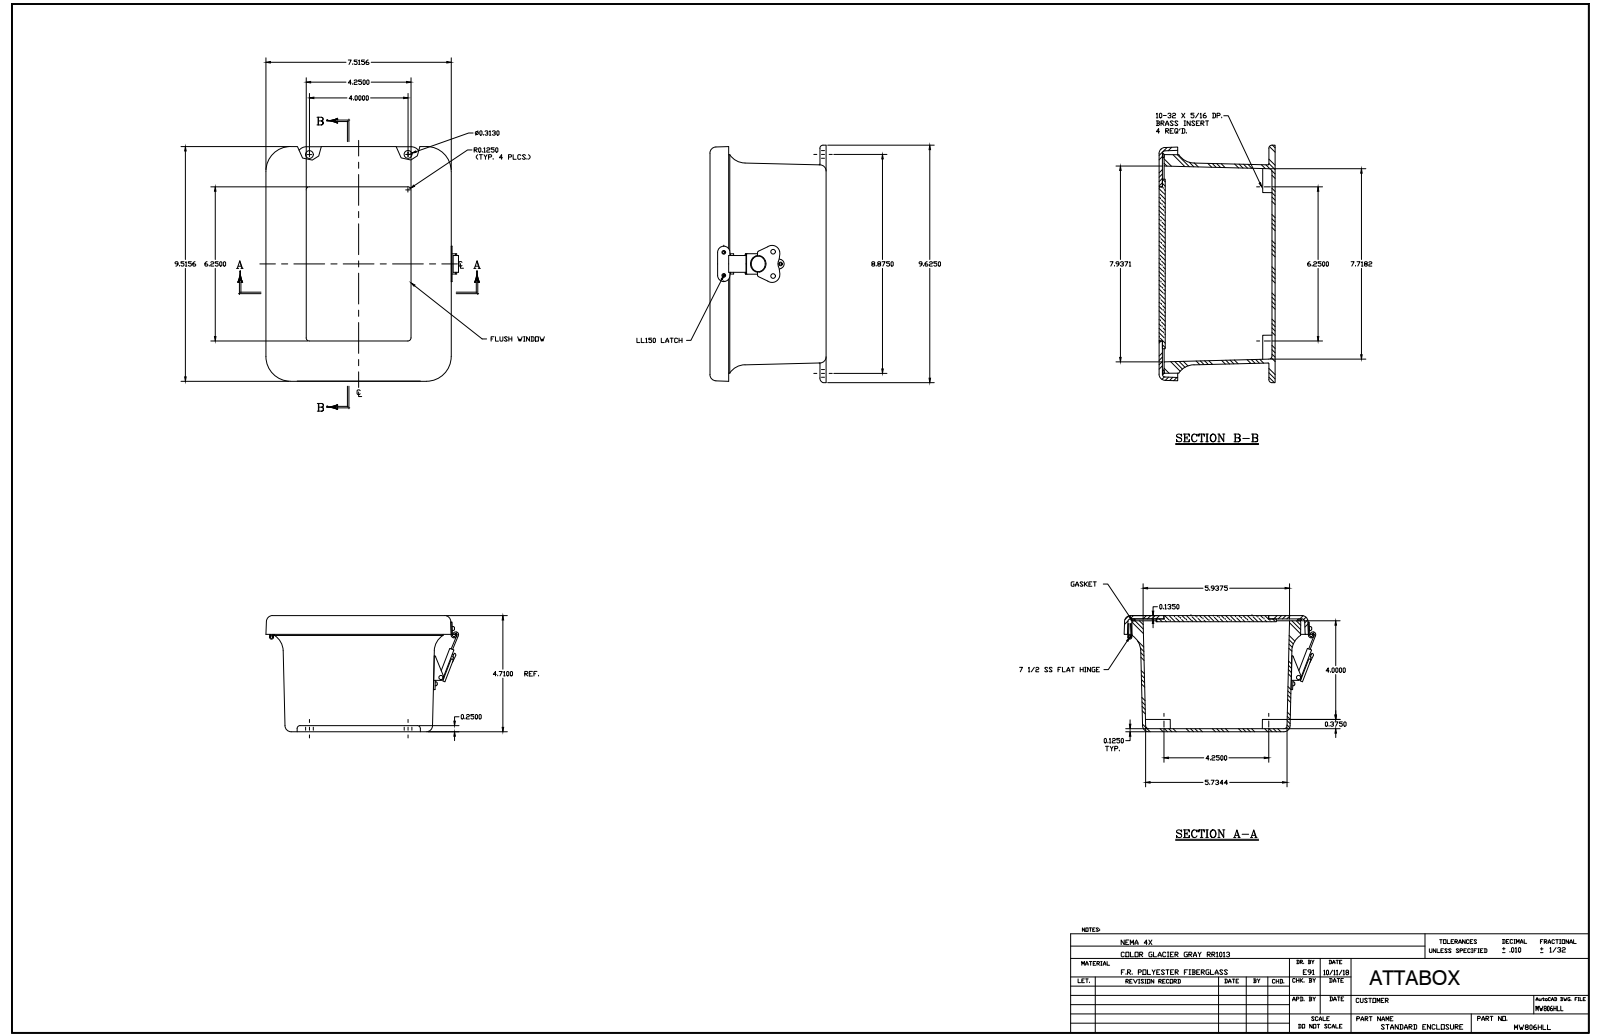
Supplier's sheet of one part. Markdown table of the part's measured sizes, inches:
| quantity | value |
| --- | --- |
| part name | MW806HLL |
| STEP written by | SolidWorks 2018 (AUTOMOTIVE_DESIGN) |
| units | inches |
| bodies | 32 solids, 784 faces (335 planar, 302 cylindrical, 147 other) |
| overall size | 9.625 × 7.756 × 4.699 |
| volume | 49.24 in³ |
| surface area | 639.4 in² |
| round holes (diameter × count) | 0.14 × 10, 0.131 × 6, 0.152 × 5, 0.156 × 4, 0.218 × 4, 0.13 × 2, 0.165 × 2, 0.197 × 2, 0.085 × 1, 0.085 × 1, 0.106 × 1, 0.118 × 1 |
| round bosses / shafts (diameter × count) | 0.25 × 10, 0.125 × 7, 0.27 × 4, 0.125 × 3, 0.583 × 1, 0.524 × 1, 0.209 × 1, 0.185 × 1 |
| partial cylindrical surfaces (radius × count) | 0.031 × 20, 0.125 × 16, 0.25 × 12, 0.079 × 10, 0.037 × 4, 0.039 × 4, 0.045 × 4, 0.047 × 4 |
| main face-to-face distances | 0.125, 0.135, 4.564, 4.699, 0.125, 0.25, 4.449, 4.439, 4.574, 0.115 |
| hole center spacings | 3.5, 1.326, 5.271, 7.249, 8.864, 0.25, 3.25, 0.469 |
